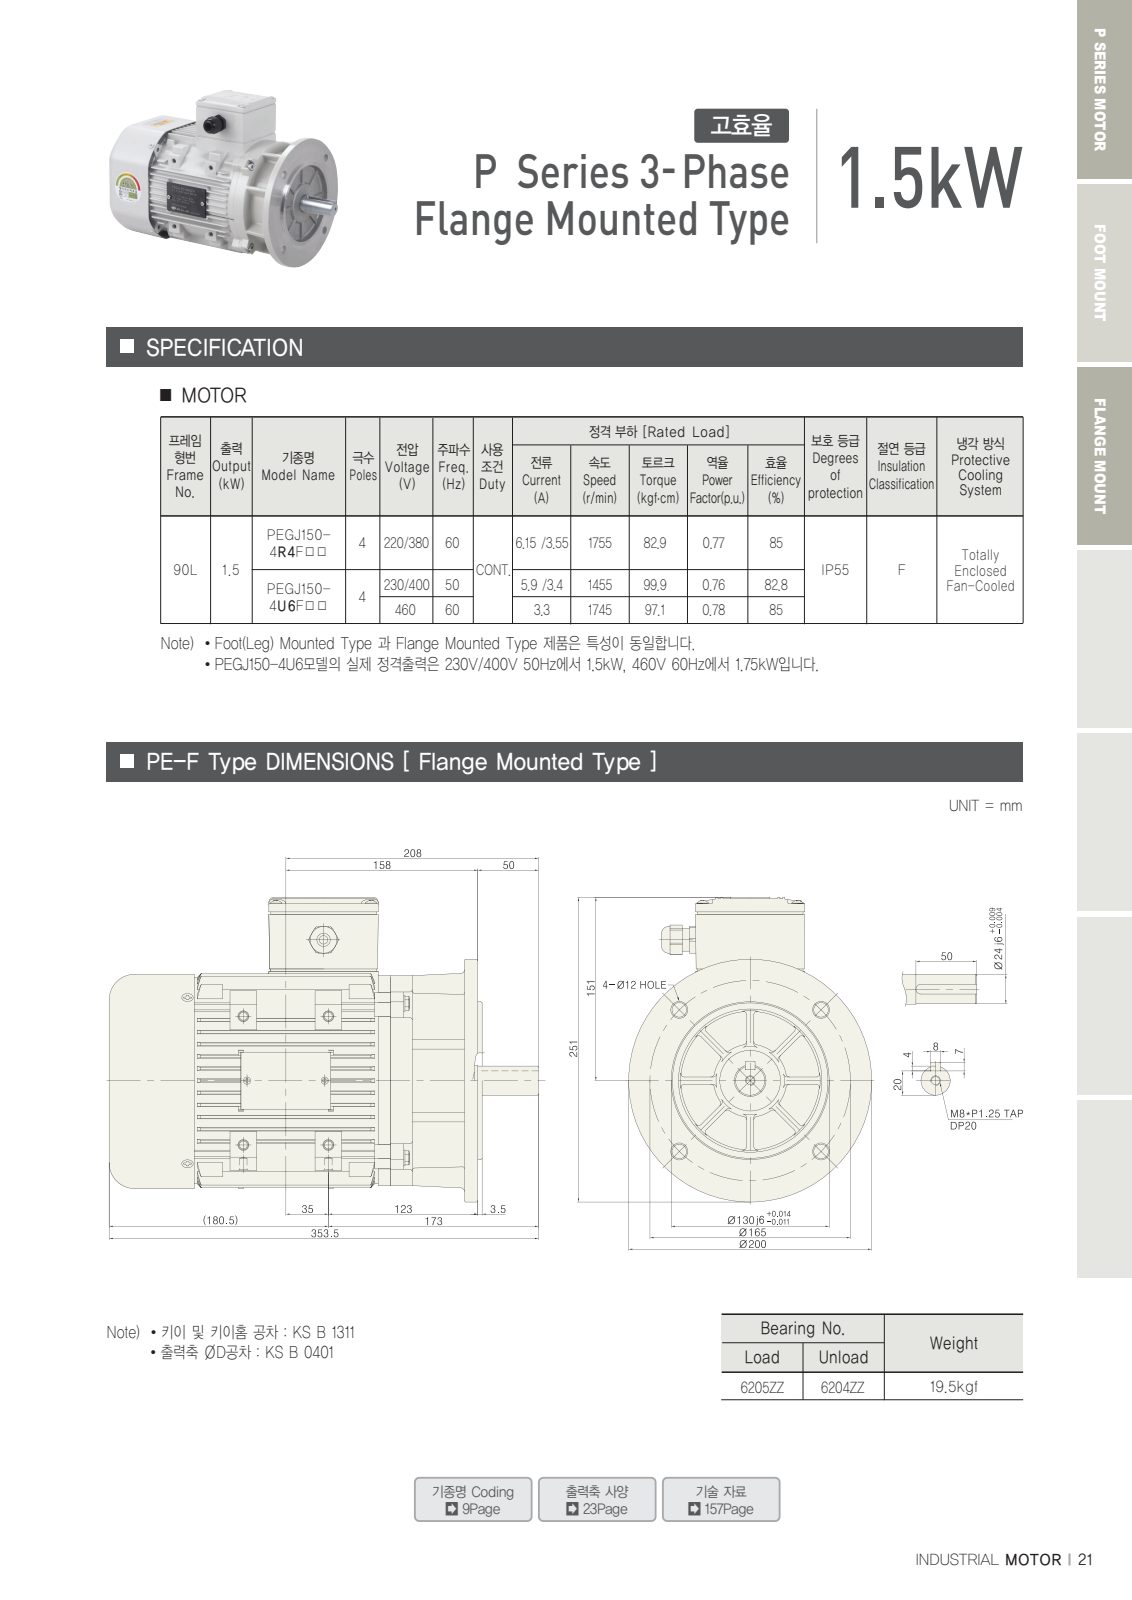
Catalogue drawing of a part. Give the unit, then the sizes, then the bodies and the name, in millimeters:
Units: millimetres
Overall size (bounding box): 353.5 × 251 × 200
Round holes (diameter × count): ⌀3.24 ×12, ⌀6.65 ×10, ⌀3.2 ×8, ⌀3.6 ×8, ⌀5 ×8, ⌀6 ×6, ⌀4.92 ×4, ⌀6.1 ×4, ⌀7 ×4, ⌀8.5 ×4, ⌀12 ×4, ⌀4.2 ×2
Round bosses / shafts (diameter × count): ⌀4 ×10, ⌀3.62 ×8, ⌀14.8 ×4, ⌀12.2 ×4, ⌀10 ×4, ⌀8 ×4, ⌀6 ×4, ⌀3.57 ×2
Partial cylindrical surfaces — rounded edges, fillets, slot ends (radius × count): R1 ×242, R0.5 ×72, R3 ×40, R5 ×36, R2 ×28, R20 ×12, R21.2 ×12, R10 ×8
Main face-to-face distances: 1.2, 1, 5, 6, 252.5, 258.5, 4, 48, 11, 47
Hole centre spacings: 53.08, 63.51, 71.34, 85.43, 122.1, 64, 7.5, 9.9
Volume: 1 997 000 mm³ · Surface area: 769 969 mm²
Bodies: 38 solids, 2885 faces (1312 planar, 1008 cylindrical, 565 other)
Part name (STEP PRODUCT): PEGJ150-4R4F; 90L 1.5kW FRAME L_T 20091120; 1.5kW 90L REAR COVER L_T 20090618; FAN COVER 20090528 (+8 more)
STEP written by: Autodesk Inventor 2011 (AUTOMOTIVE_DESIGN)
